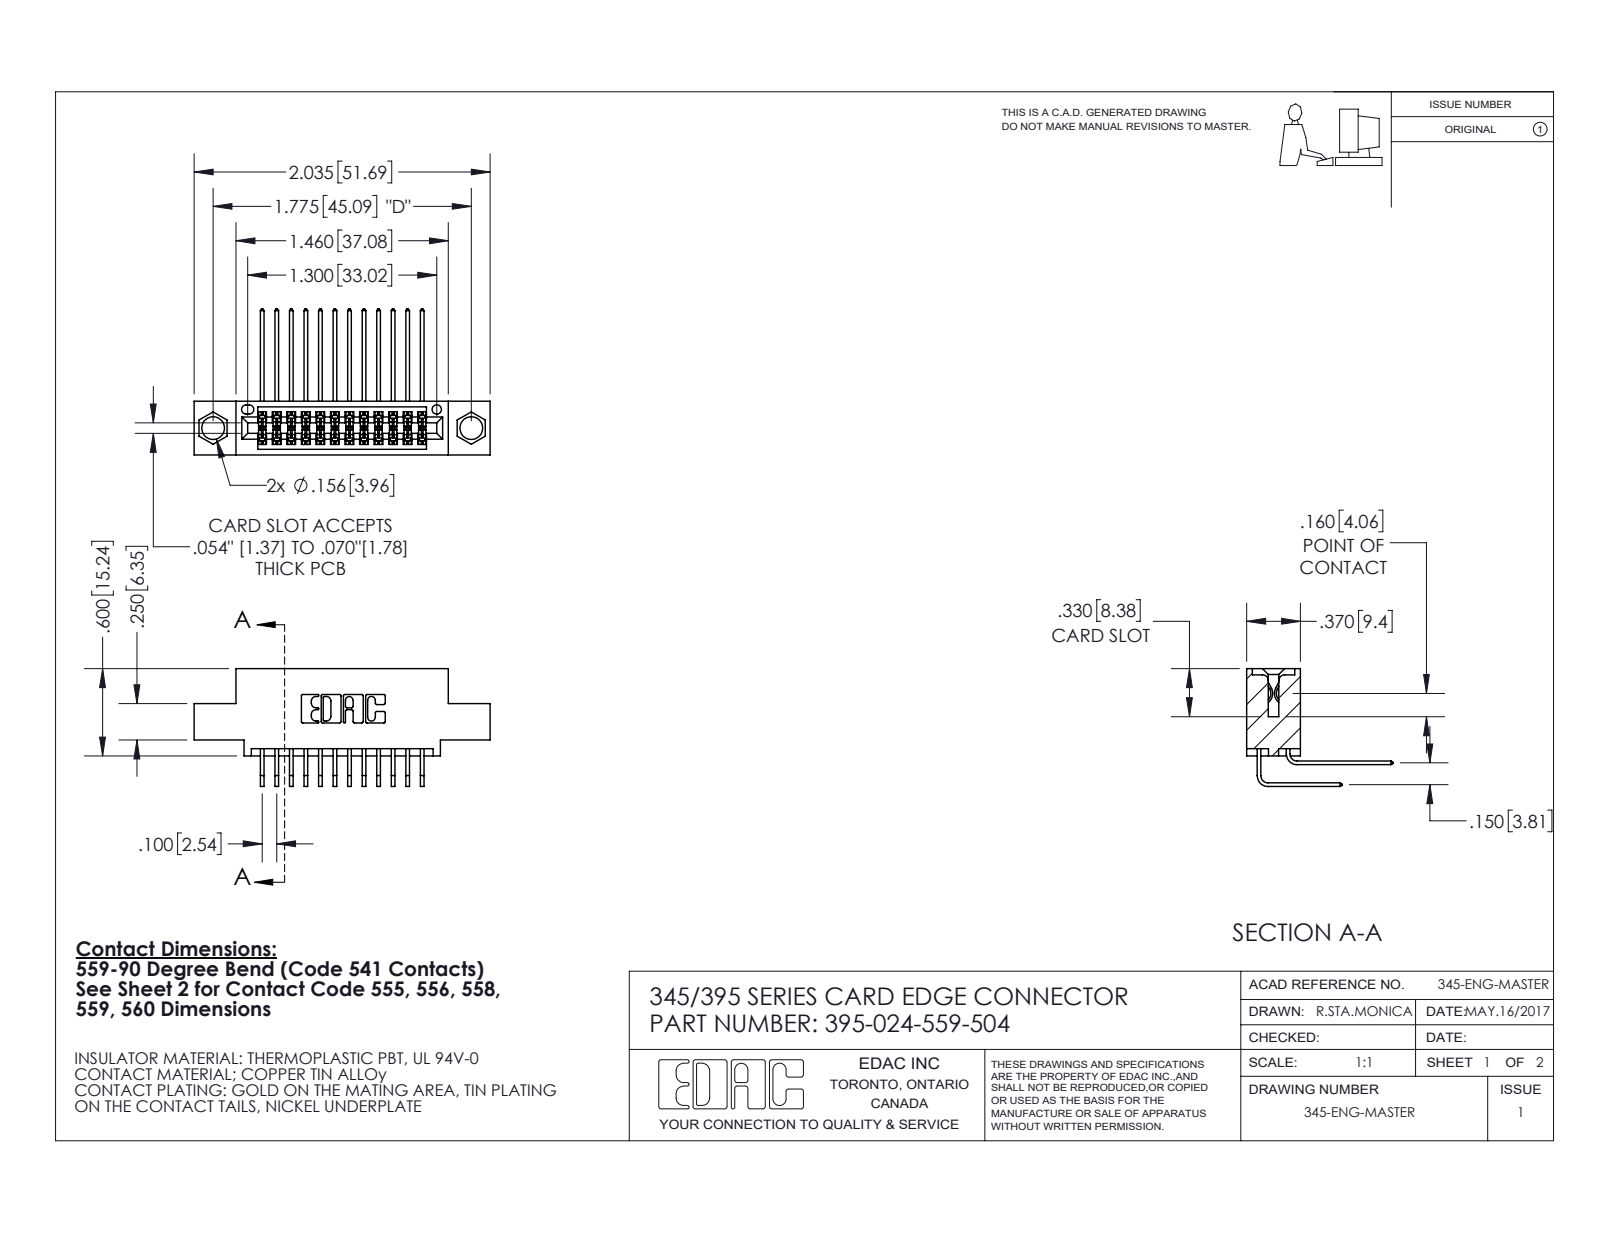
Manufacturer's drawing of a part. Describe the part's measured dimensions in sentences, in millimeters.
The part is named "345-292-001_558 559 Tail - 1; 395-024-559-504; 345-292-001_559 Tail - 2; 345 Part_0.110 Offset - 0.156 Dia-TI". Its 3-D file was written by "SolidWorks 2020 (CONFIG_CONTROL_DESIGN)". It is 25 solids with 1392 faces: 938 planar, 454 cylindrical and 0 other. Overall it measures 51.7 by 25.5 by 20.5 millimeters. Its volume is 4 700 cubic millimeters and its surface area 6 961 square millimeters. Round holes: 2 of diameter 4, 1 of diameter 1.6. Partial cylindrical surfaces (rounded edges, fillets, slot ends): 36 of radius 0.2, 22 of radius 0.3, 6 of radius 0.2, 6 of radius 0.8, 3 of radius 0.7, 2 of radius 0.4, 2 of radius 0.5, 2 of radius 0.6. The main face-to-face distances are 1.8, 7.6, 5.1, 9.4, 2.5, 6.9, 0.6, 5.7, 3.8, 2.5. The hole center spacings are 6.9, 39.2, 45.1.
